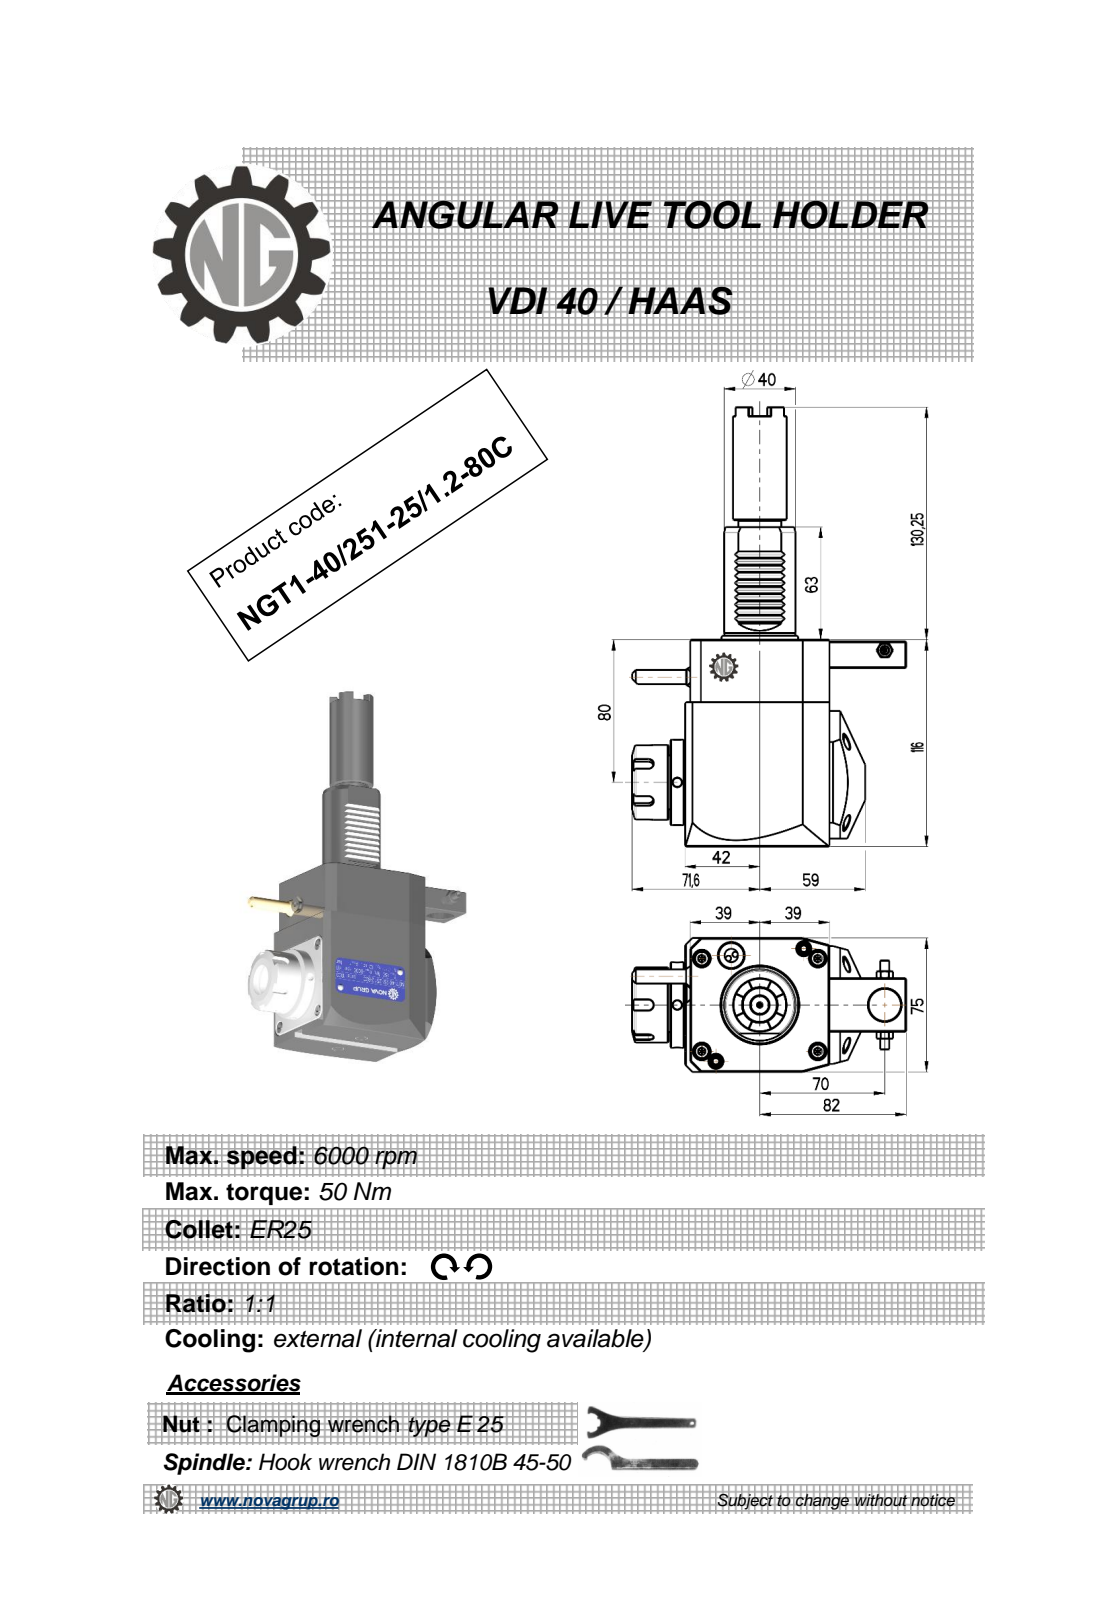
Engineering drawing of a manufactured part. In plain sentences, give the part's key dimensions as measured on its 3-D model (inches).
The part is named "NGT1_40_251_25_1_2_80C". Its 3-D file was written by "PRO/ENGINEER BY PARAMETRIC TECHNOLOGY CORPORATION, 2010280 (CONFIG_CONTROL_DESIGN)". It is 1 solid with 482 faces: 227 planar, 92 cylindrical and 163 other. Overall it measures 9.695 by 6.047 by 3.016 inches. Its volume is 55.4 cubic inches and its surface area 121.6 square inches. Round holes: 3 of diameter 0.197, 1 of diameter 0.118, 1 of diameter 0.165, 1 of diameter 0.374, 1 of diameter 0.709, 1 of diameter 0.768, 1 of diameter 0.799. Round bosses or shafts: 1 of diameter 1.89, 1 of diameter 1.654, 1 of diameter 1.575, 1 of diameter 1.476, 1 of diameter 1.299, 1 of diameter 1.181, 1 of diameter 0.945, 1 of diameter 0.394. Partial cylindrical surfaces (rounded edges, fillets, slot ends): 12 of radius 0.01, 10 of radius 0.012, 6 of radius 0.008, 5 of radius 0.118, 1 of radius 0.02, 1 of radius 1.575. The main face-to-face distances are 2.953, 4.567, 3.189, 0.118, 3.071, 0.11, 3.181, 0.039, 0.433, 0.886. The hole center spacings are 0.824, 1.821, 2.407, 2.756, 2.854, 4.577, 5.425.
